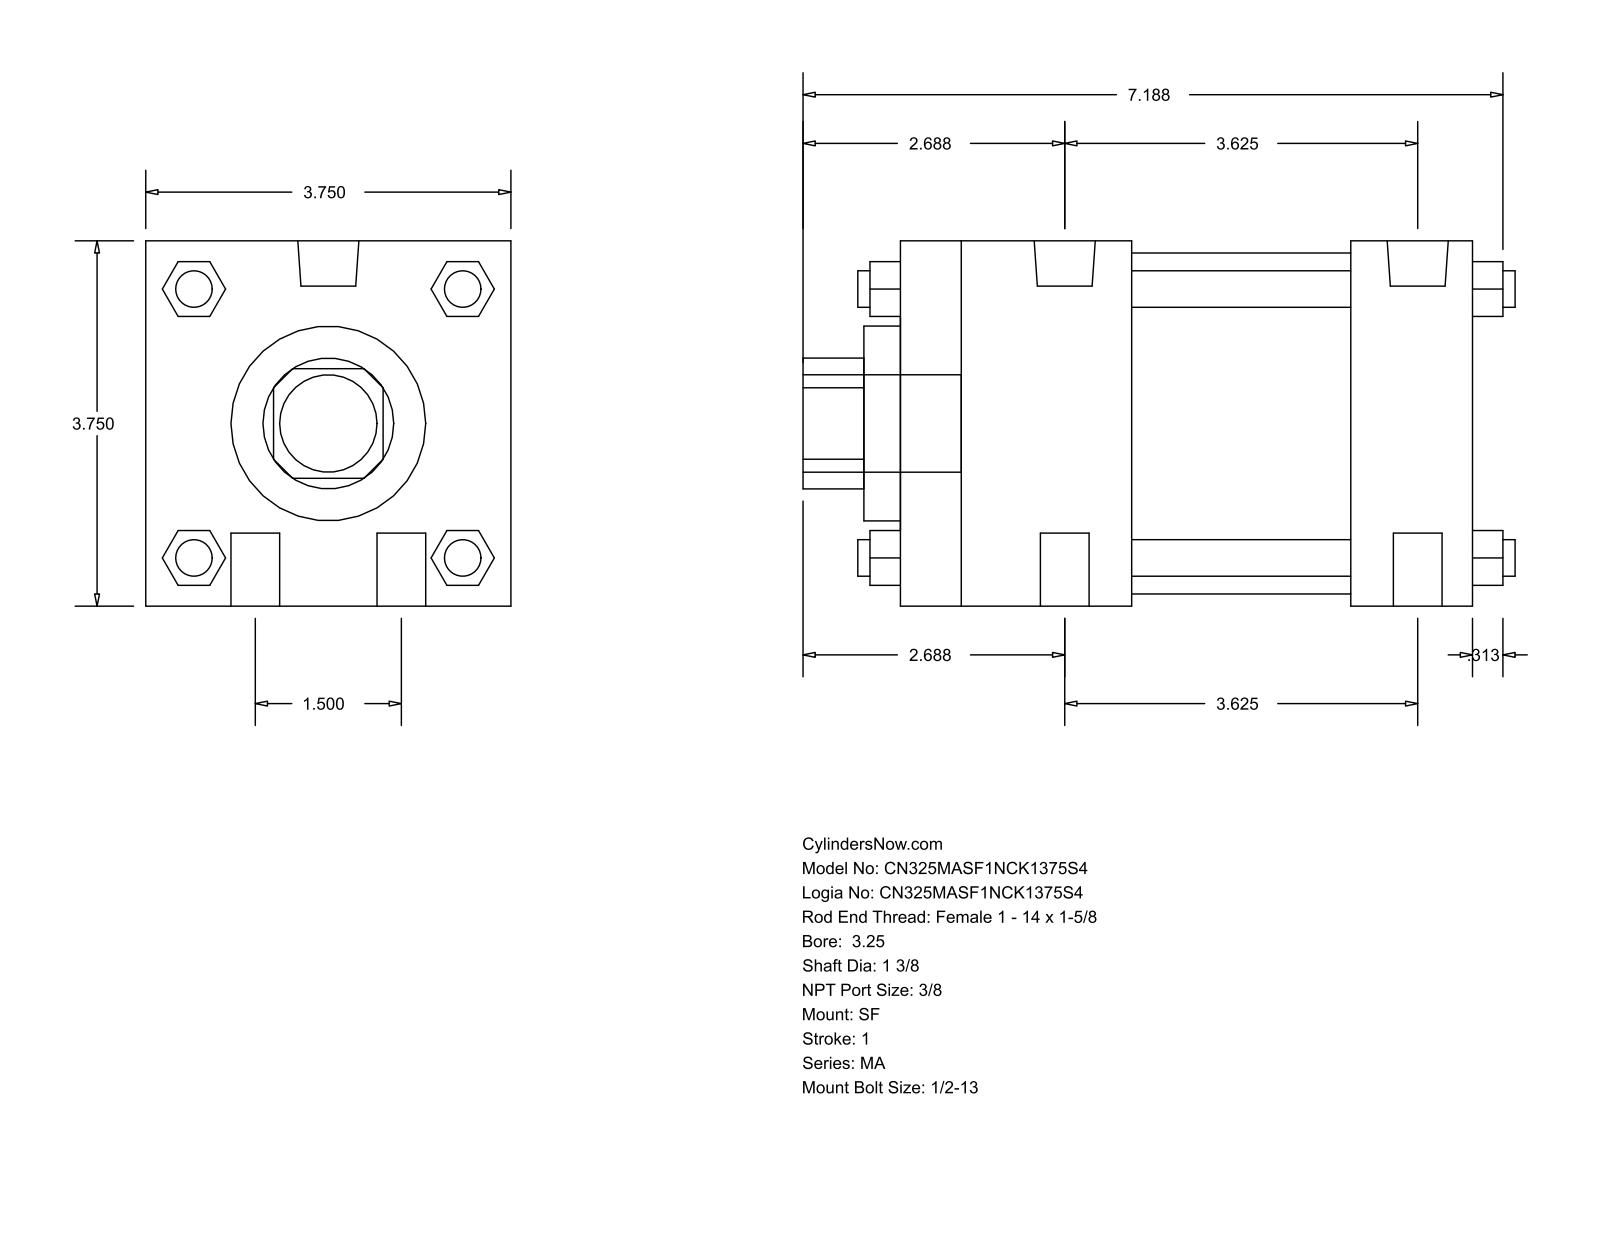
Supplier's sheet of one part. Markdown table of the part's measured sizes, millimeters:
| quantity | value |
| --- | --- |
| part name | MA_SF__0325_1.375 |
| STEP written by | GSSL Pune (CONFIG_CONTROL_DESIGN) |
| units | millimeters |
| bodies | 0 solids, 124 faces (94 planar, 30 cylindrical, 0 other) |
| overall size | 185.74 × 95.25 × 95.25 |
| round holes (diameter × count) | 34.92 × 1, 50.8 × 1, 88.9 × 1 |
| round bosses / shafts (diameter × count) | 12.7 × 4, 9.53 × 4, 15.93 × 2, 11.11 × 2, 25.4 × 1 |
| partial cylindrical surfaces (radius × count) | 17.06 × 1 |
| main face-to-face distances | 95.24, 149.22, 117.48, 31.74, 60.32, 57.16, 88.9, 9.52, 69.84, 127 |
